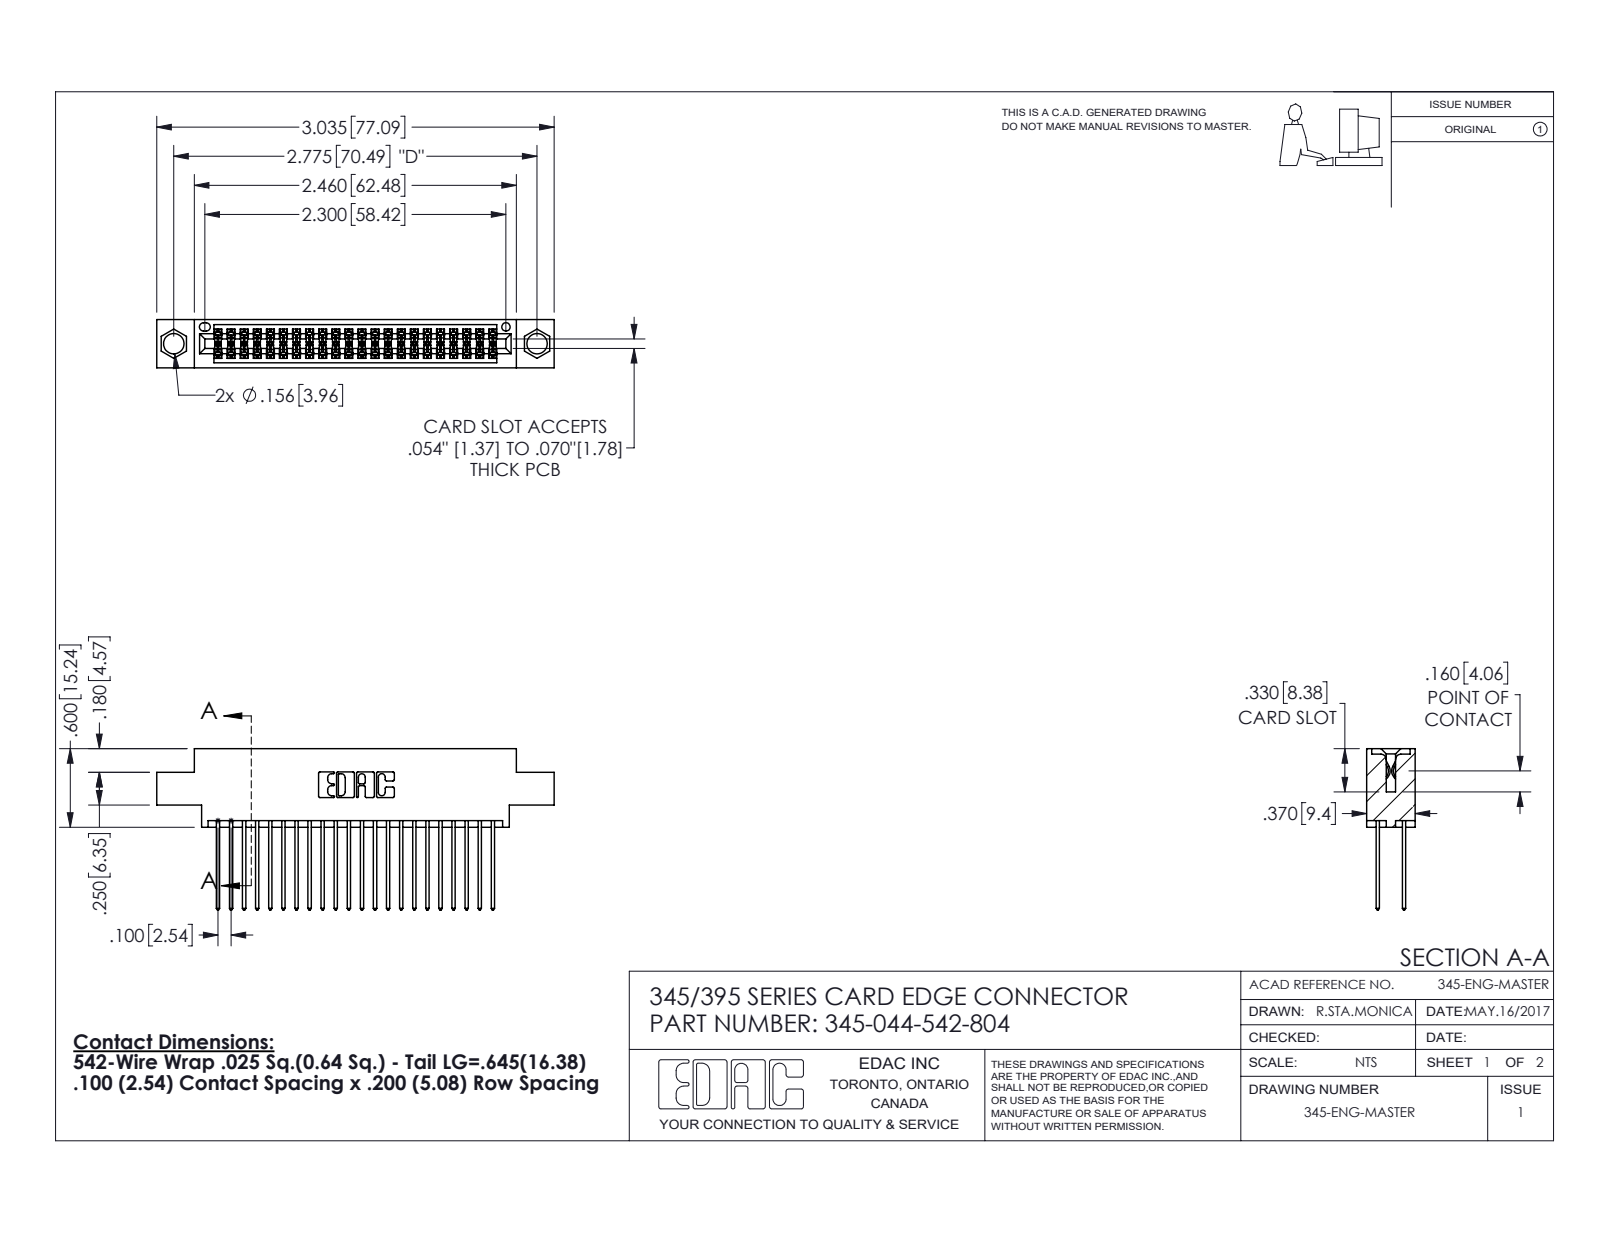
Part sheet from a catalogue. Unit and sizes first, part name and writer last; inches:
Units: inches
Overall size (bounding box): 3.035 × 1.232 × 0.37
Round holes (diameter × count): ⌀0.156 ×2, ⌀0.064 ×1
Partial cylindrical surfaces — rounded edges, fillets, slot ends (radius × count): R0.006 ×67, R0.01 ×44, R0.01 ×22, R0.007 ×6, R0.031 ×6, R0.026 ×3, R0.014 ×2, R0.019 ×2
Main face-to-face distances: 0.072, 0.298, 0.2, 0.098, 0.272, 0.025, 0.37, 0.225, 0.175, 0.149
Hole centre spacings: 0.27, 2.541, 2.775
Volume: 0.445 in³ · Surface area: 17.58 in²
Bodies: 45 solids, 2344 faces (1550 planar, 794 cylindrical, 0 other)
Part name (STEP PRODUCT): 345 Part_0.170 Offset - 0.156 Dia-TI; 345-292-001_345-293-142; 345-044-542-804
STEP written by: SolidWorks 2020 (CONFIG_CONTROL_DESIGN)
